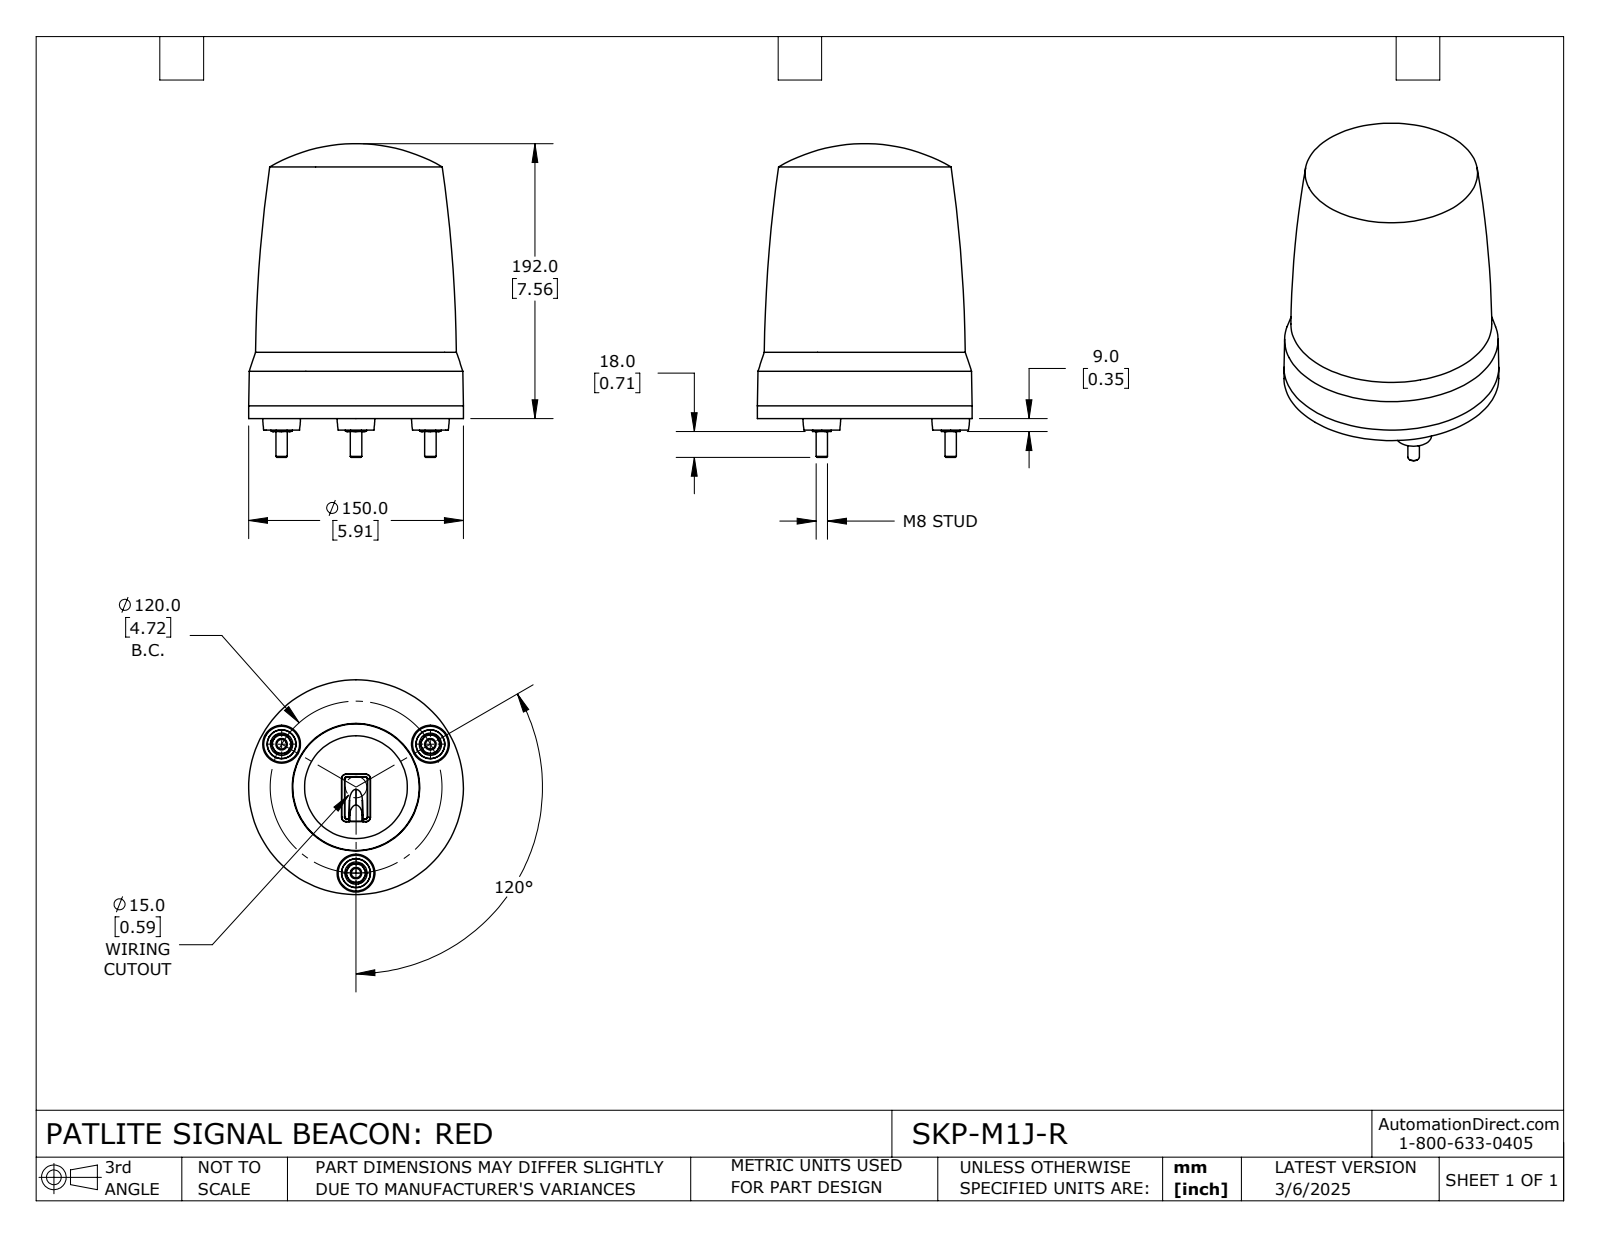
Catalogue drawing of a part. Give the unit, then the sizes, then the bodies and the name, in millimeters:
Units: millimetres
Overall size (bounding box): 219 × 150 × 150
Round bosses / shafts (diameter × count): ⌀15.5 ×3, ⌀8 ×3, ⌀150 ×1
Main face-to-face distances: 32.7, 8, 40.7, 13, 7.1, 0.9, 33.6, 1.6, 36.05, 41.55
Volume: 2 538 000 mm³ · Surface area: 119 026 mm²
Bodies: 1 solid, 144 faces (49 planar, 14 cylindrical, 81 other)
Part name (STEP PRODUCT): SKP-M1J-R
STEP written by: SolidWorks 2024 (CONFIG_CONTROL_DESIGN)
